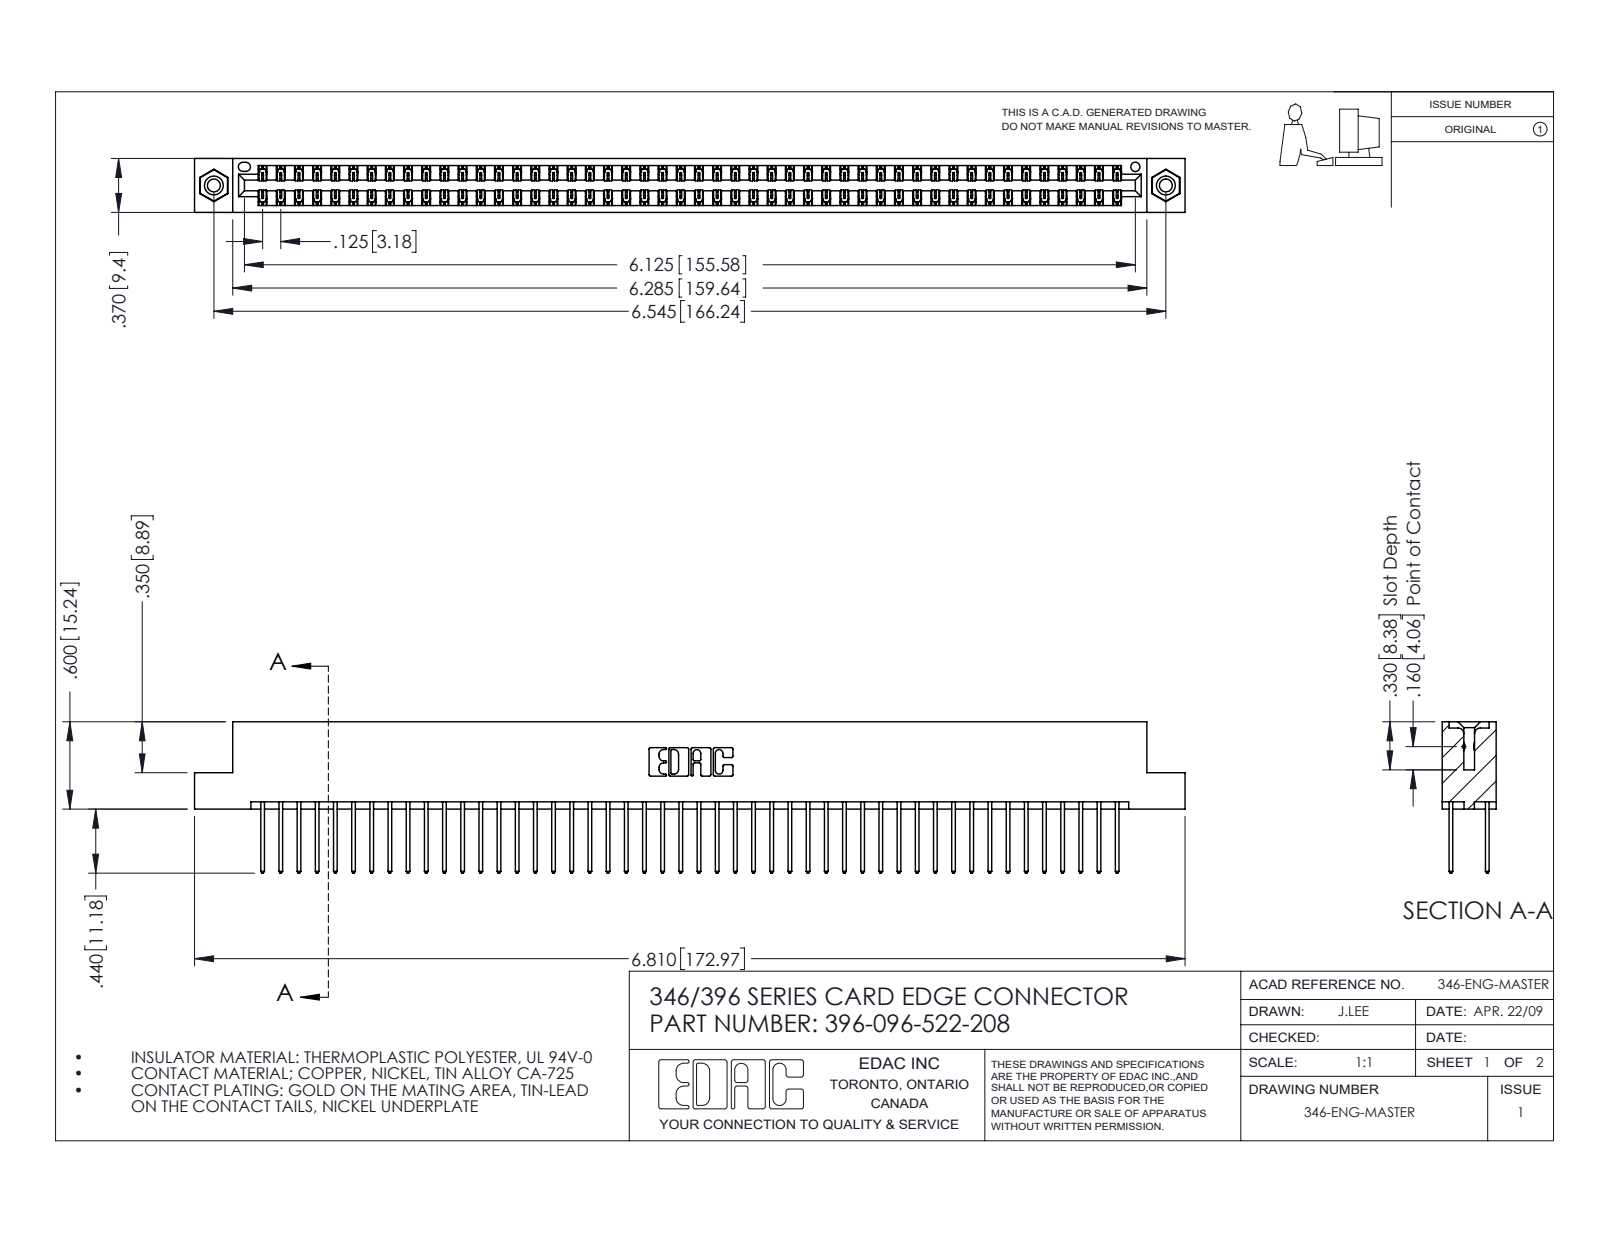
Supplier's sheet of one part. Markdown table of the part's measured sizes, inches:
| quantity | value |
| --- | --- |
| part name | 345-292-001_345-293-122; 345-250-001_345-250-003-102; 346 Part_Flush Mounting Lugs - 0.156 Dia-TI; 396-096-522-208 |
| STEP written by | SolidWorks 2016 (CONFIG_CONTROL_DESIGN) |
| units | inches |
| bodies | 99 solids, 5174 faces (3468 planar, 1690 cylindrical, 16 other) |
| overall size | 6.81 × 1.04 × 0.37 |
| volume | 1.047 in³ |
| surface area | 38.49 in² |
| round holes (diameter × count) | 0.089 × 2, 0.125 × 2, 0.156 × 2, 0.064 × 1 |
| round bosses / shafts (diameter × count) | 0.155 × 2 |
| partial cylindrical surfaces (radius × count) | 0.006 × 144, 0.01 × 96, 0.01 × 22, 0.007 × 6, 0.031 × 6, 0.026 × 3, 0.014 × 2, 0.022 × 2 |
| main face-to-face distances | 0.048, 0.322, 0.25, 0.072, 0.298, 0.025, 0.37, 0.275, 0.148, 0.222 |
| hole center spacings | 0.246, 6.336, 6.545 |
